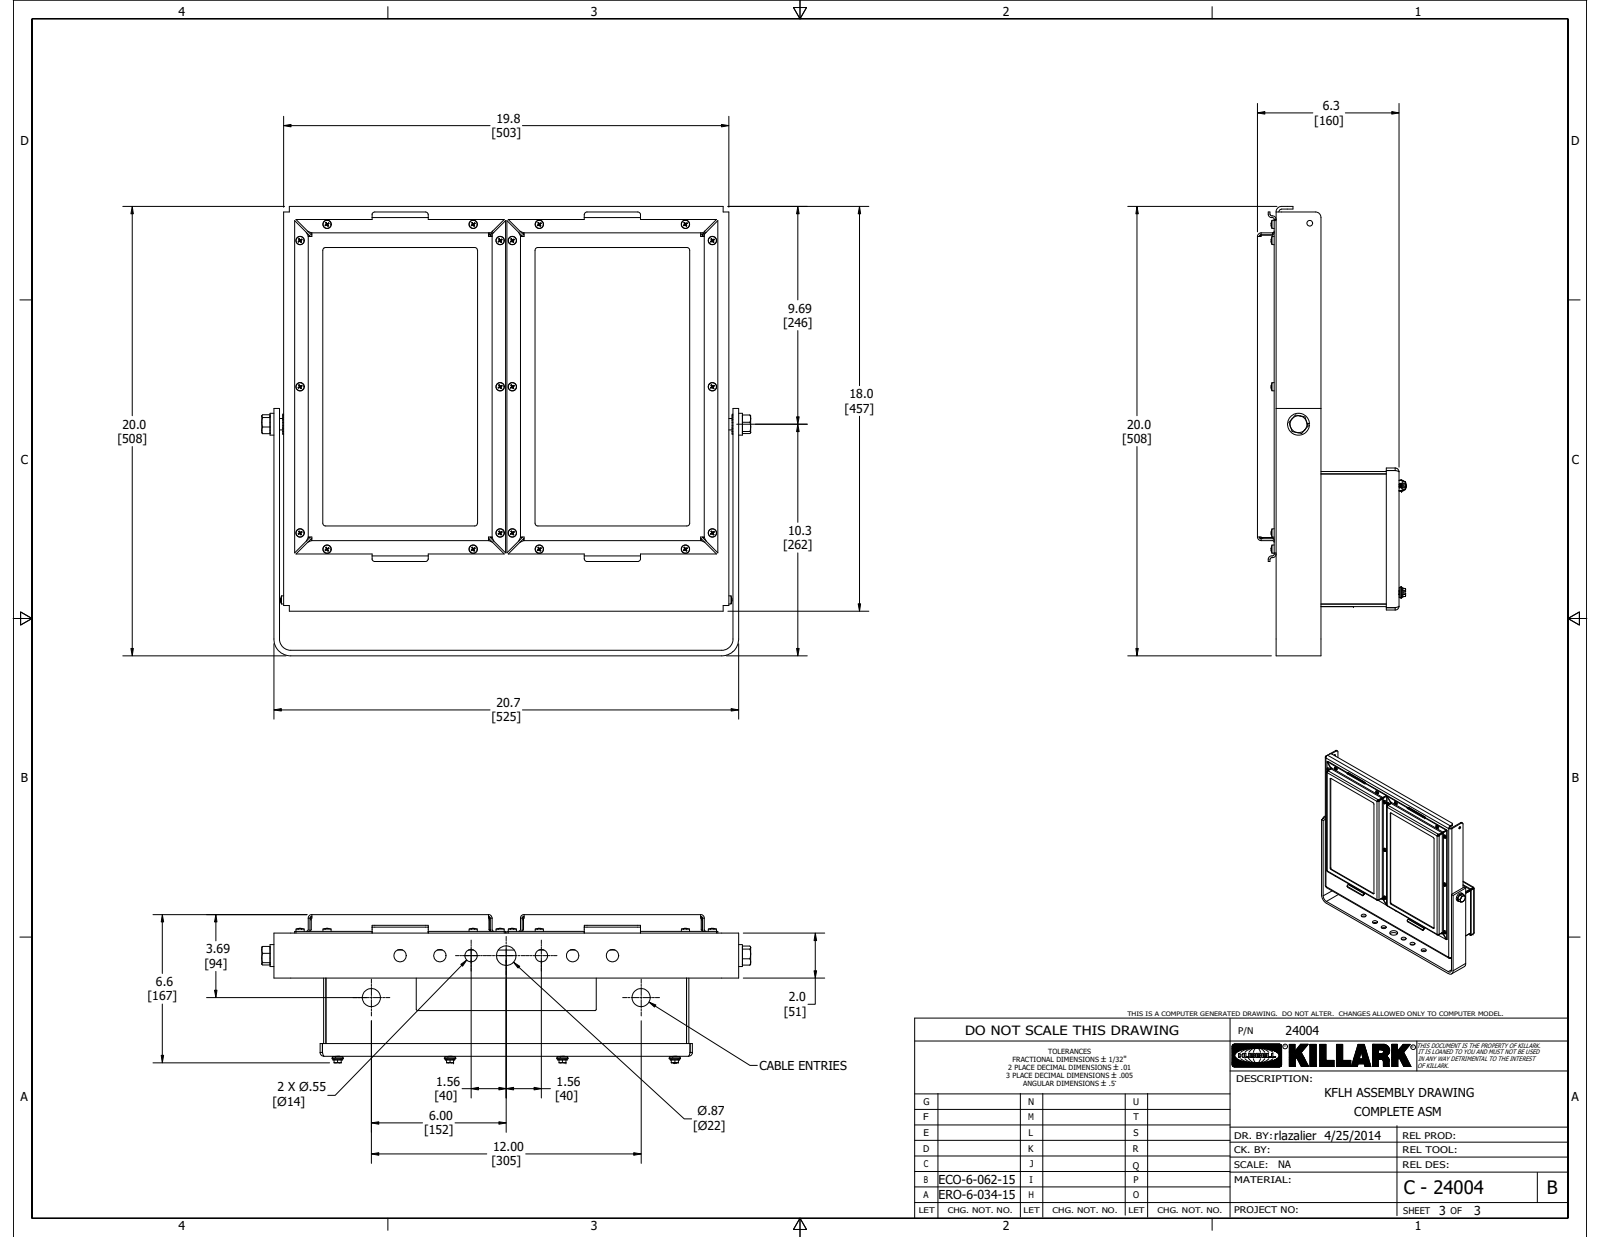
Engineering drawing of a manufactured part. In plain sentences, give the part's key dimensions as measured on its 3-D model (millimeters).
The part is named "23591-3; FHS-832-6; FHS-832-16; 23293 (+8 more)". Its 3-D file was written by "Autodesk Inventor 2016 (AUTOMOTIVE_DESIGN)". It is 281 solids with 9218 faces: 4459 planar, 2256 cylindrical and 2503 other. Overall it measures 552.27 by 507.66 by 167.34 millimeters. Its volume is 4 164 000 cubic millimeters and its surface area 3 118 000 square millimeters. Round holes: 46 of diameter 2.67, 31 of diameter 6.35, 30 of diameter 3.17, 30 of diameter 3.66, 28 of diameter 4.5, 20 of diameter 4.29, 16 of diameter 4.76, 10 of diameter 4.14, 8 of diameter 2.62, 8 of diameter 4.37, 8 of diameter 5.08, 8 of diameter 5.94. Round bosses or shafts: 30 of diameter 2.84, 29 of diameter 4.83, 20 of diameter 7.67, 10 of diameter 5.12, 8 of diameter 11.68, 8 of diameter 11.43, 8 of diameter 10.52, 8 of diameter 7.54. Partial cylindrical surfaces (rounded edges, fillets, slot ends): 126 of radius 0.64, 96 of radius 0.1, 96 of radius 0.15, 82 of radius 3.17, 51 of radius 1.02, 45 of radius 6.35, 41 of radius 0.3, 40 of radius 0.61. The main face-to-face distances are 3.17, 18.13, 2.66, 21.3, 11.11, 7.94, 14.96, 7.02, 10.19, 129.03. The hole center spacings are 165.1, 239.82, 35.57, 185.96, 196.44, 268.15, 279.93, 291.16.
